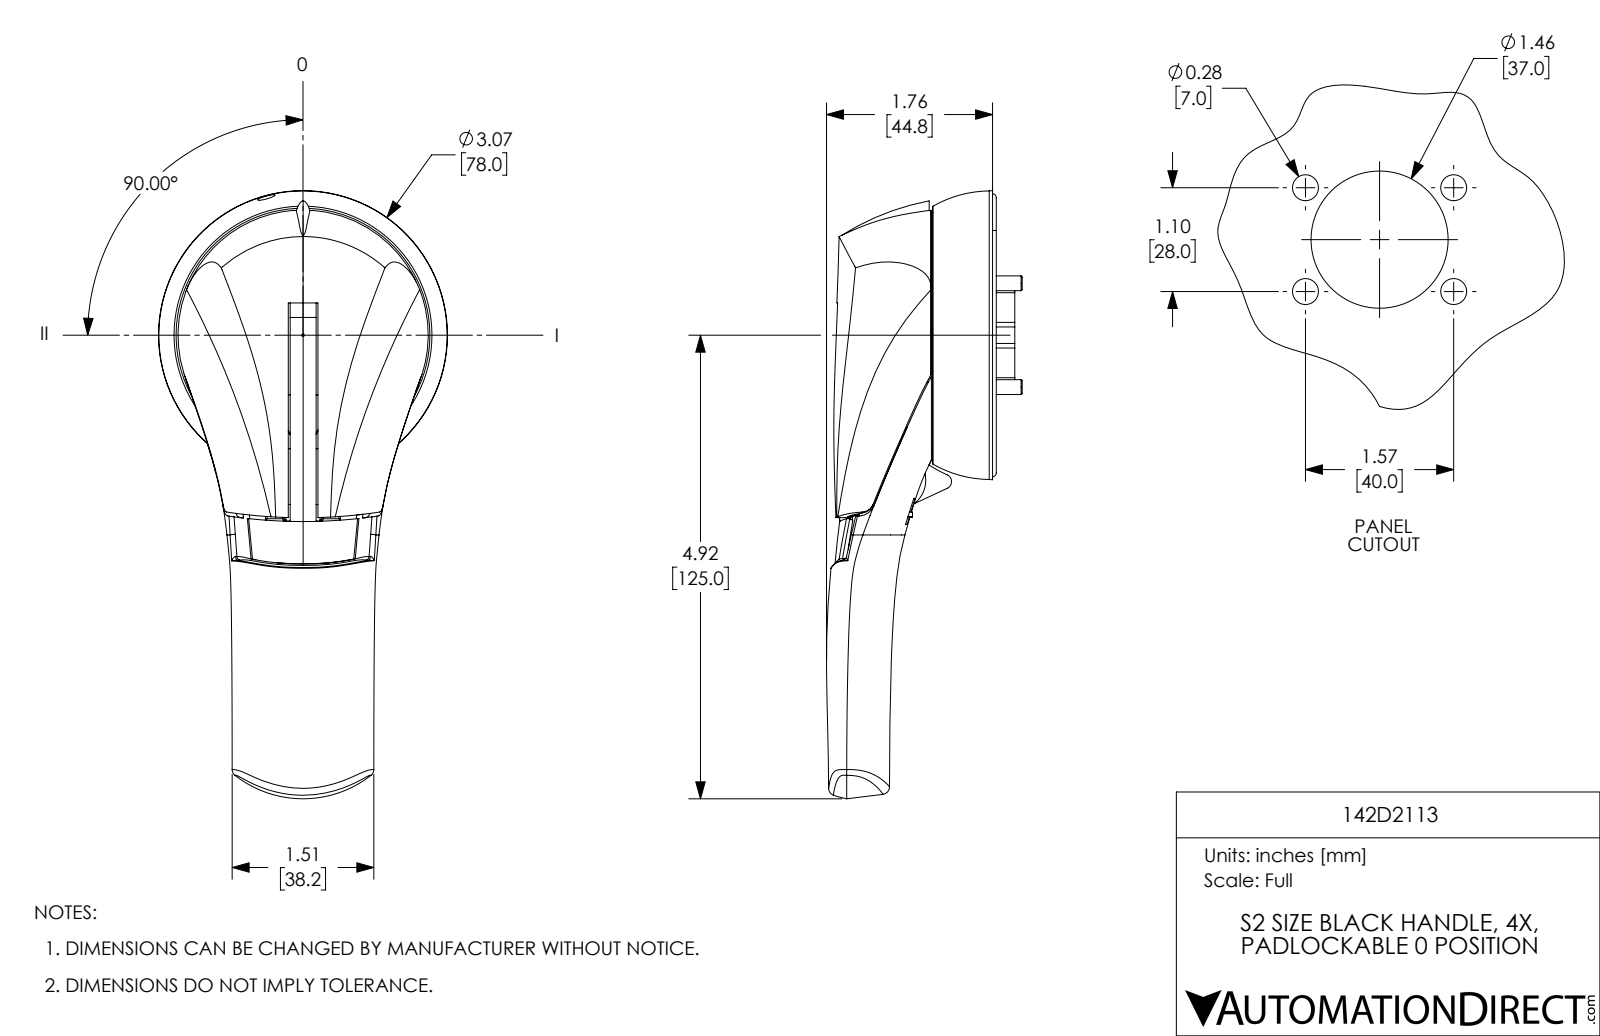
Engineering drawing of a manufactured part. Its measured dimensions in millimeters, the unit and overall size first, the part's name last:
Units: millimetres
Overall size (bounding box): 164 × 78 × 52.8
Round holes (diameter × count): ⌀4 ×6, ⌀8.6 ×4, ⌀10.8 ×4, ⌀0.8 ×3, ⌀4.3 ×2, ⌀9.2 ×2, ⌀3 ×1, ⌀4.8 ×1, ⌀76 ×1
Round bosses / shafts (diameter × count): ⌀0.5 ×11, ⌀8.5 ×4, ⌀8 ×4, ⌀2.3 ×3, ⌀1.8 ×3, ⌀5.8 ×2, ⌀71.6 ×1, ⌀68.6 ×1
Partial cylindrical surfaces — rounded edges, fillets, slot ends (radius × count): R0.3 ×221, R0.4 ×20, R0.9 ×20, R0.8 ×15, R1 ×4, R0.6 ×3, R138.1 ×3, R2 ×2
Main face-to-face distances: 0.6, 17.8, 18.1, 17.5, 0.9, 2.6, 7, 4.4, 6.2, 1.2
Hole centre spacings: 24.4, 7.8, 17, 27.9, 28, 30.6, 40, 47.8
Volume: 155 900 mm³ · Surface area: 56 330 mm²
Bodies: 8 solids, 1516 faces (810 planar, 548 cylindrical, 158 other)
Part name (STEP PRODUCT): 142D2113
STEP written by: SolidWorks 2017 (AUTOMOTIVE_DESIGN)
